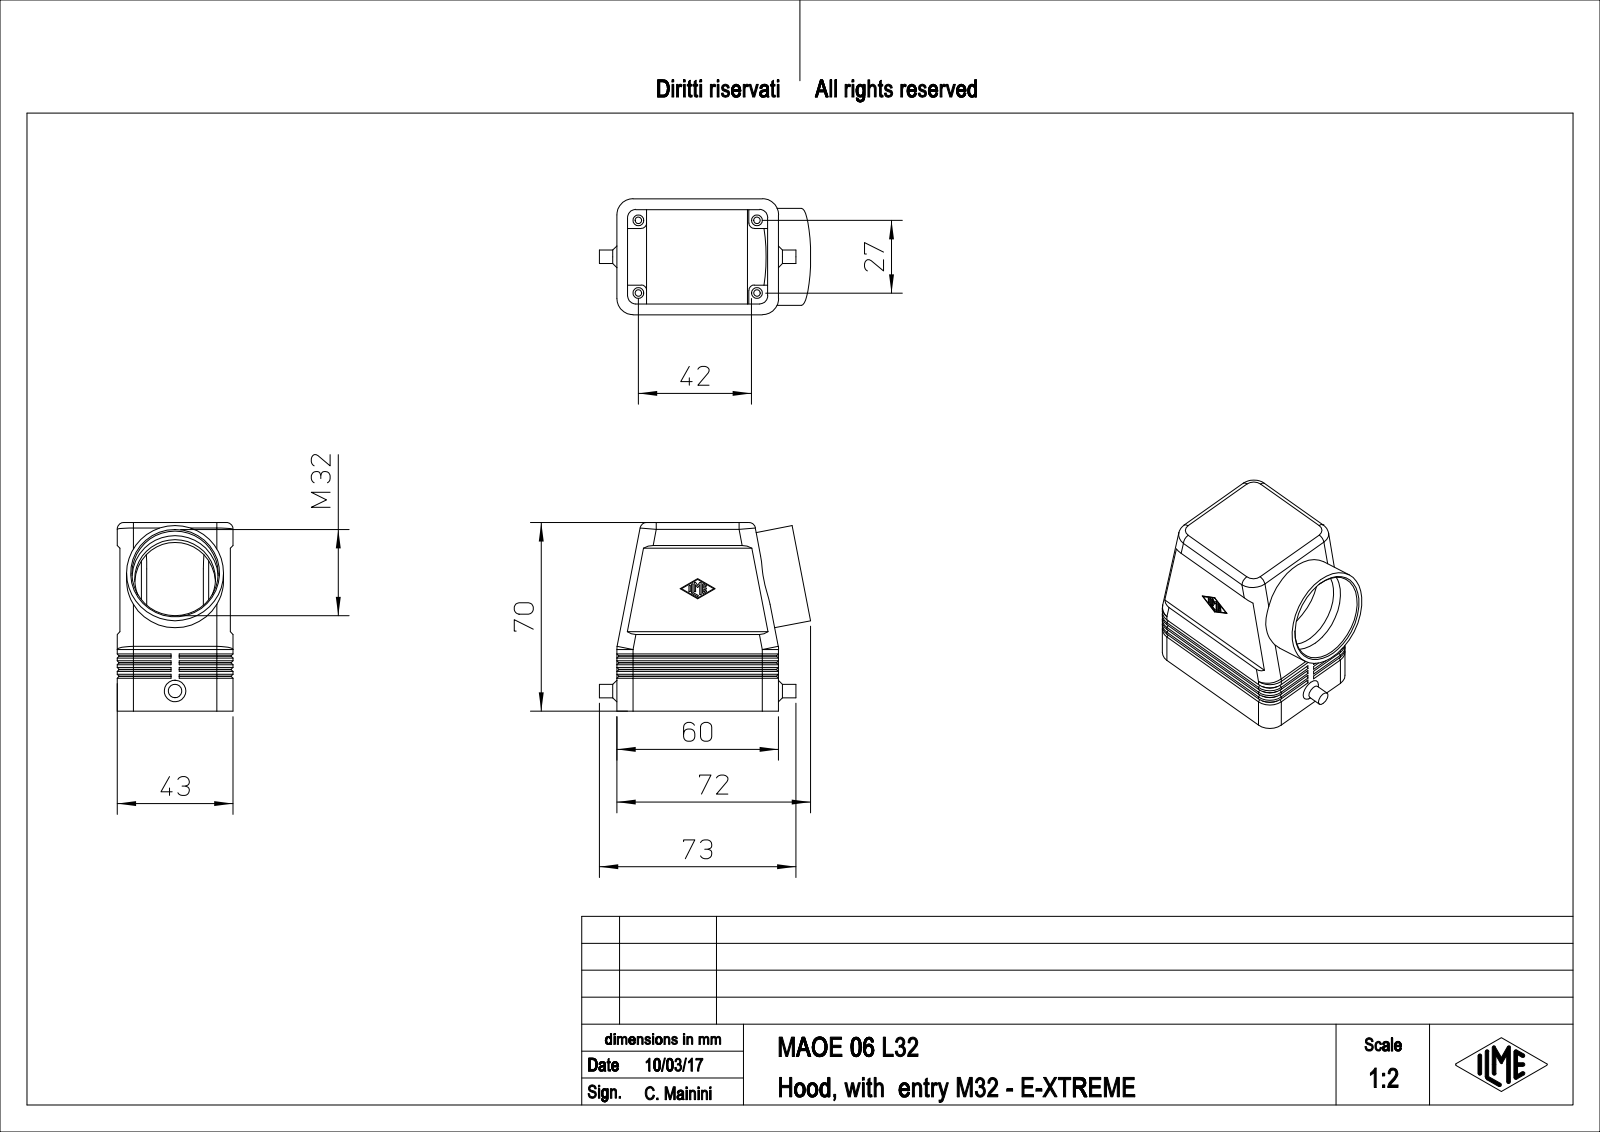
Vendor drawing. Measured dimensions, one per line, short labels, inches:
name: MAOE_06_L32
written by: PTC Creo Elements/Direct Modeling 19.0E 27-Jun-2016 (C) Parametric Technology GmbH (AUTOMOTIVE_DESIGN)
unit: in
bodies: 1 solid, 336 faces (181 planar, 99 cylindrical, 56 other)
size: 3.089 × 2.756 × 1.693
volume: 3.42 in³; area: 47.24 in²
holes: 4× ⌀0.097, 4× ⌀0.157, 1× ⌀1.181, 1× ⌀1.26
bosses: 1× ⌀1.417, 1× ⌀0.197
rounds: 14× R0.01, 10× R0.236, 4× R0.079, 4× R0.098, 4× R0.118, 4× R0.209
face distances: 0.157, 1.496, 0.118, 1.378, 0.039, 1.535, 1.654, 1.614, 0.276, 0.197
hole spacings: 1.063, 1.732, 2.032
